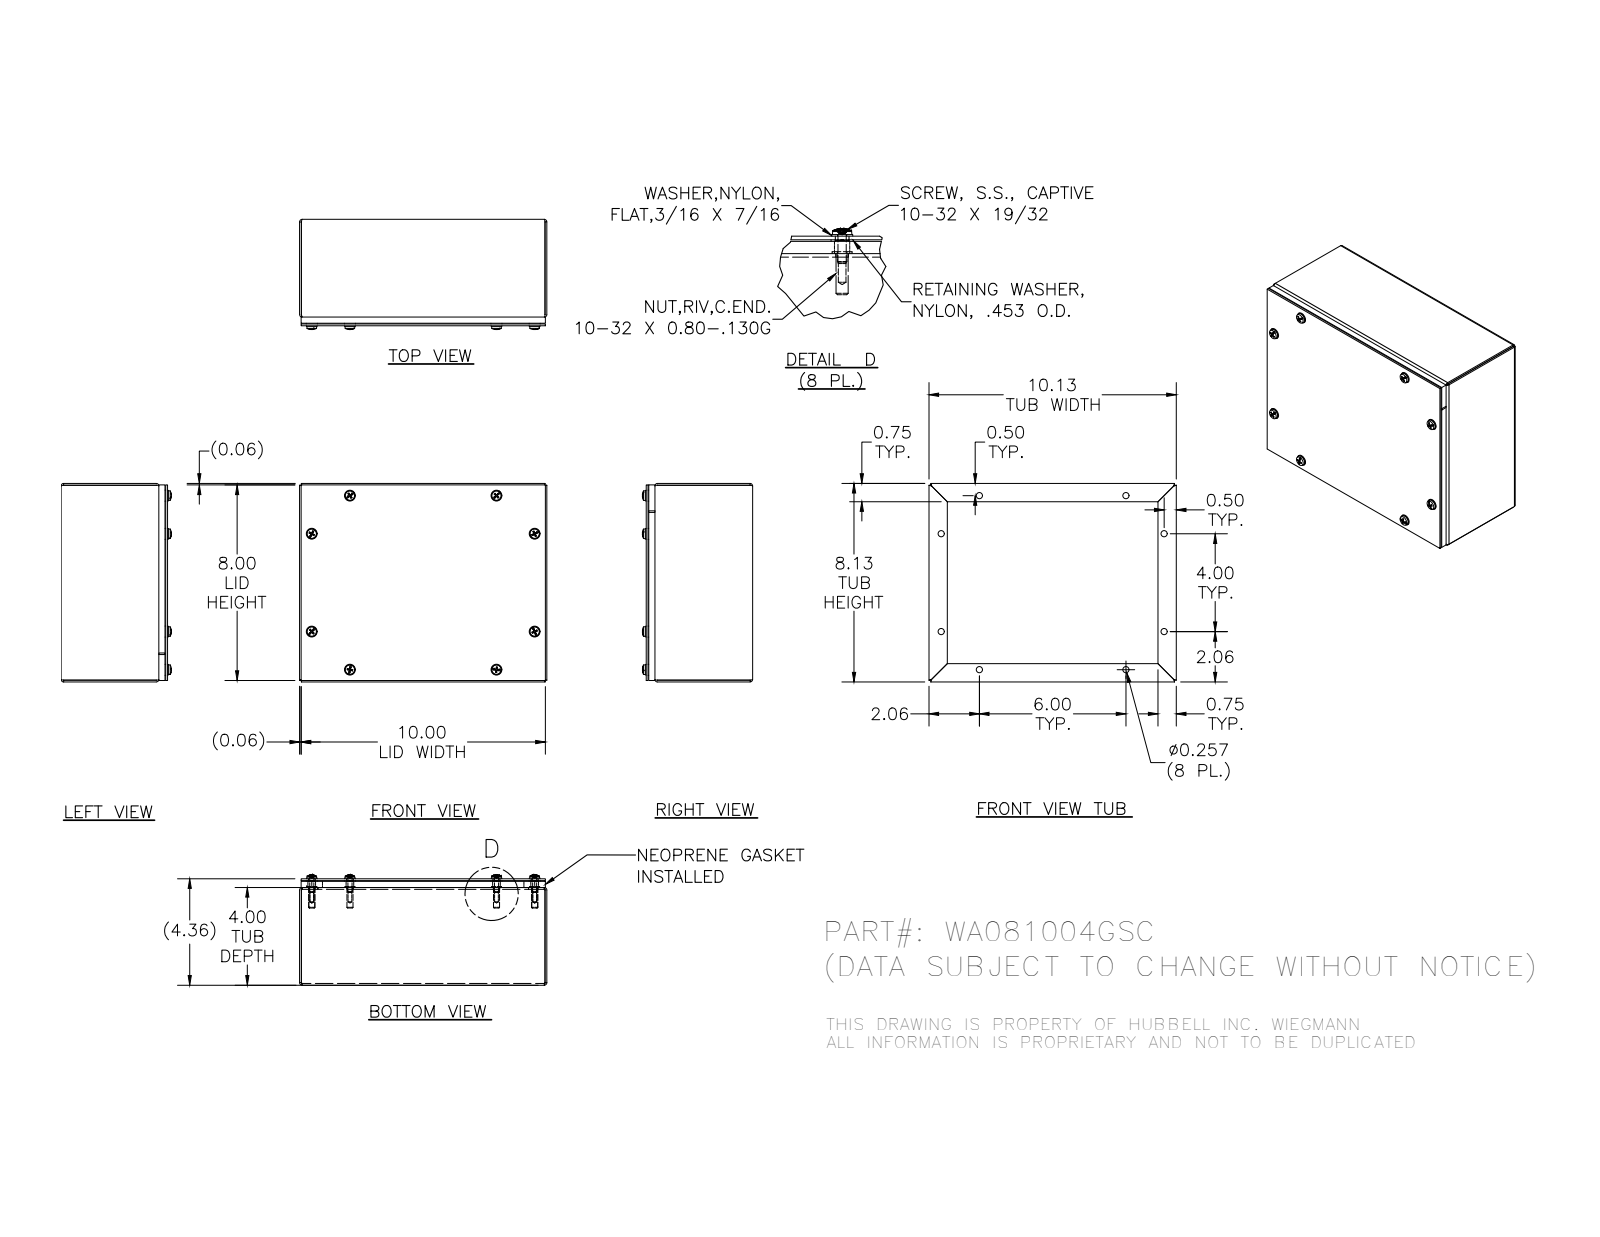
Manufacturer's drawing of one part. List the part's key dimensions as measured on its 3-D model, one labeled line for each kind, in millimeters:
Part name (STEP PRODUCT): 37210; 316296; 39077; 34984 (+4 more)
STEP written by: SolidWorks 2014 (AUTOMOTIVE_DESIGN)
Units: millimetres
Bodies: 36 solids, 892 faces (420 planar, 240 cylindrical, 232 other)
Overall size (bounding box): 257.2 × 206.4 × 114.6
Volume: 513 700 mm³ · Surface area: 484 200 mm²
Round holes (diameter × count): ⌀4 ×8, ⌀4.8 ×8, ⌀5 ×8, ⌀6.5 ×8, ⌀7.1 ×8, ⌀7.1 ×8, ⌀8 ×8
Round bosses / shafts (diameter × count): ⌀11.5 ×8, ⌀11.1 ×8, ⌀10.3 ×8, ⌀6.3 ×8, ⌀4.2 ×8
Partial cylindrical surfaces — rounded edges, fillets, slot ends (radius × count): R0.8 ×8, R2.3 ×8, R2.7 ×8
Main face-to-face distances: 1.9, 108.8, 110.6, 106.9, 204.5, 9, 99.7, 255.3, 7.2, 101.6
Hole centre spacings: 56.1, 101.6, 152.4, 146.8, 196.1, 238.4, 146.8, 196.1
